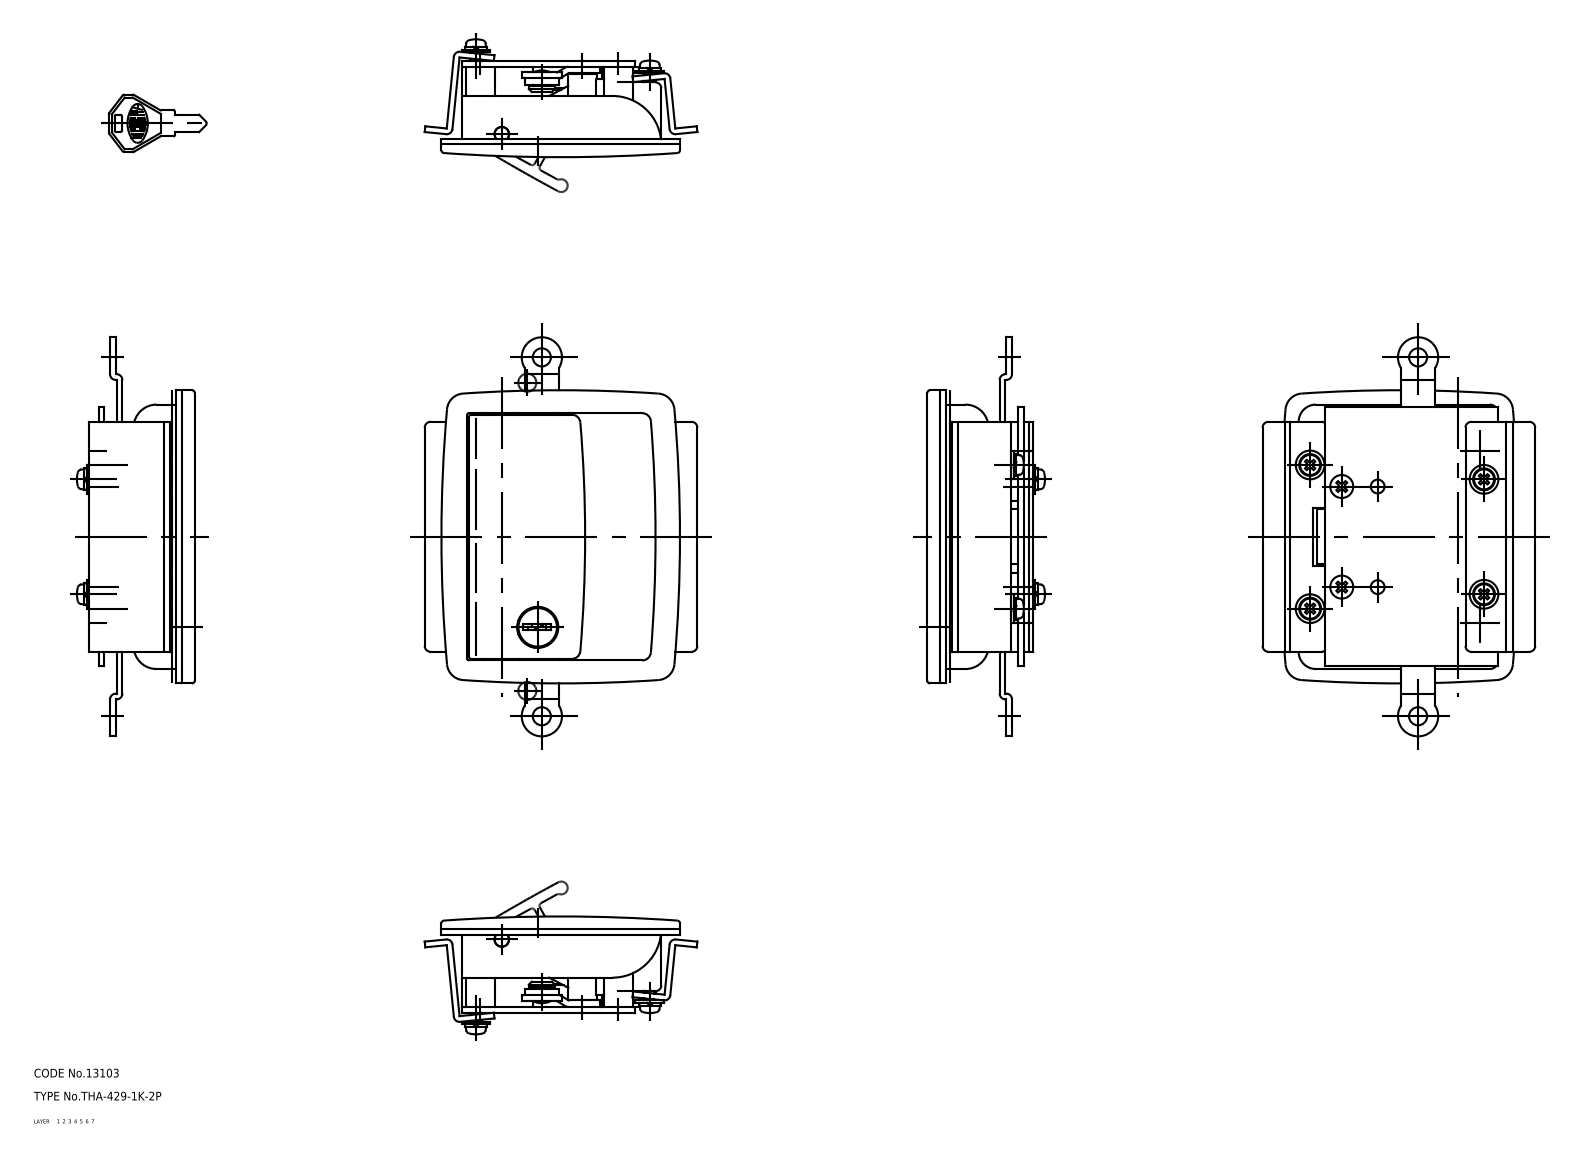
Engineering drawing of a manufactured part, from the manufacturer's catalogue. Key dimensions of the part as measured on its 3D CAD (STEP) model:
Part name (STEP PRODUCT): link_C_mr; link_C; link_B; link_A (+8 more)
STEP written by: CADfix (AUTOMOTIVE_DESIGN)
Units: millimetres
Bodies: 17 solids, 634 faces (0 planar, 0 cylindrical, 634 other)
Overall size (bounding box): 138.88 × 103.19 × 94.85
Volume: 97 112 mm³ · Surface area: 85 175 mm²
